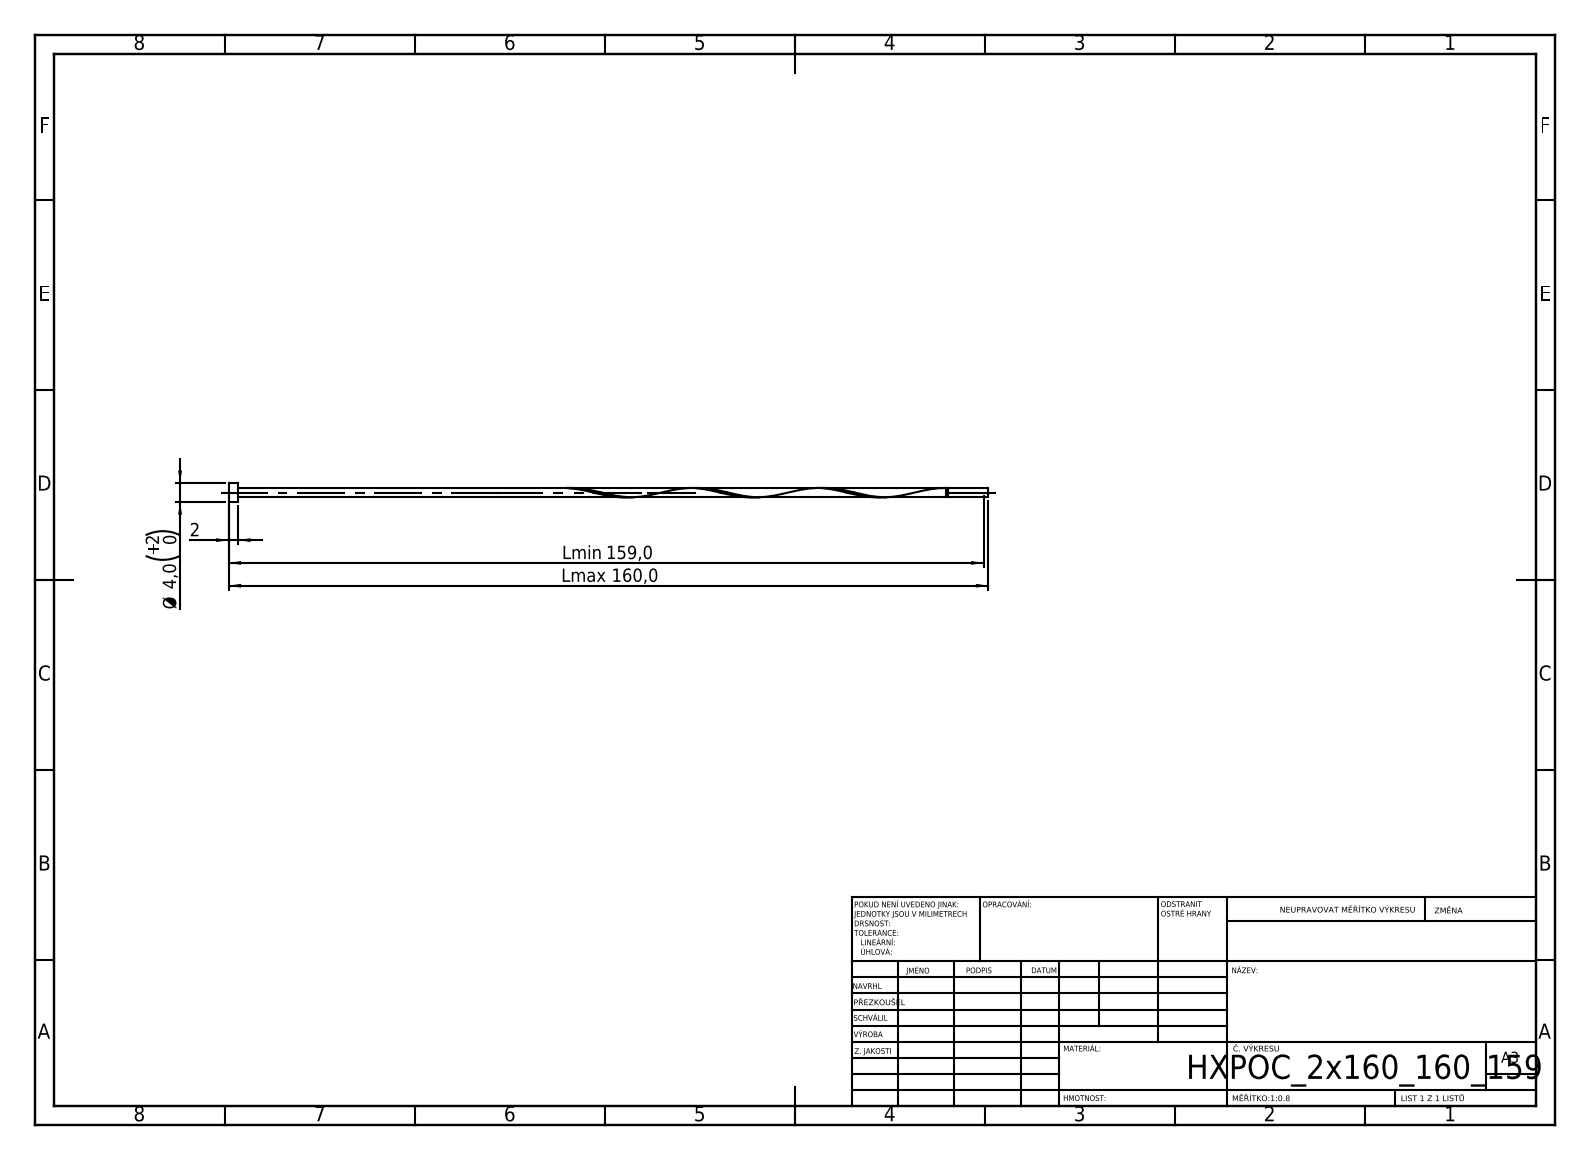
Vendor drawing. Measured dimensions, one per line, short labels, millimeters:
written by: SolidWorks 2019 (CONFIG_CONTROL_DESIGN)
unit: mm
bodies: 1 solid, 16 faces (6 planar, 9 cylindrical, 1 other)
size: 160 × 4 × 4
volume: 628 mm³; area: 1 395 mm²
bosses: 1× ⌀4, 1× ⌀2, 1× ⌀1.6
face distances: 2, 160, 158, 151.49, 149.49, 8.51, 151.09, 149.09, 0.4, 8.91
